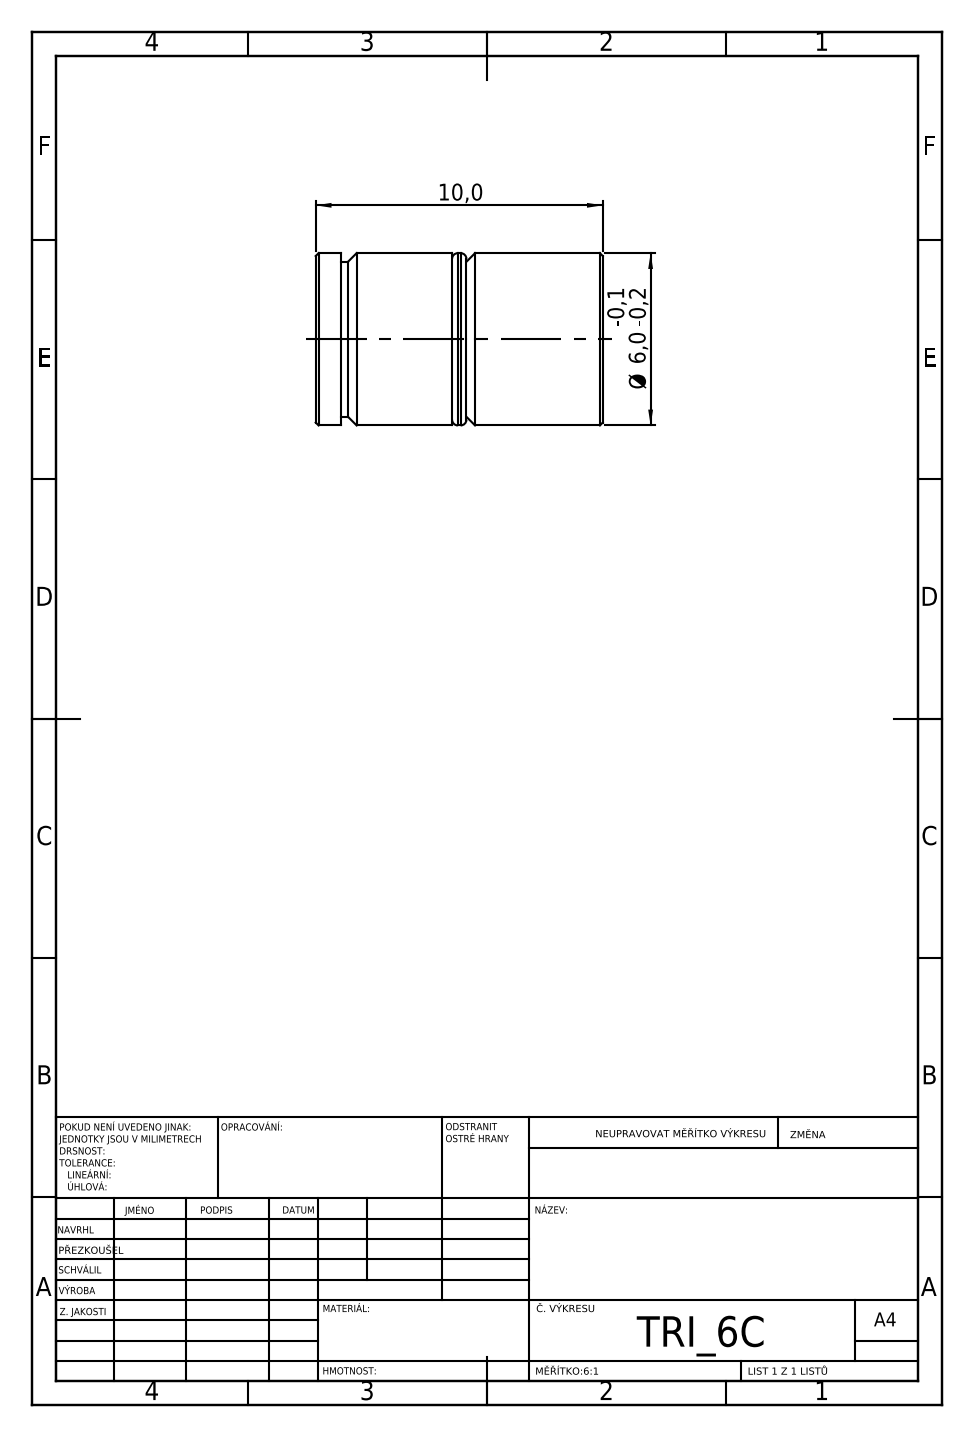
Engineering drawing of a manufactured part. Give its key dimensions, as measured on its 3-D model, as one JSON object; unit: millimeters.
{"step_written_by": "SolidWorks 2019 (CONFIG_CONTROL_DESIGN)", "units": "millimeters", "bodies": {"solids": 2, "faces": 43, "planar": 19, "cylindrical": 12, "other": 12}, "overall_size": [10, 6, 6], "volume_mm3": 275, "surface_area_mm2": 332, "round_bosses_or_shafts": [[6, 1], [5.4, 1]], "face_to_face_distances": [4.75, 5.25, 0.5, 3.75, 4.25, 9, 1, 10, 4.2, 9.13]}
